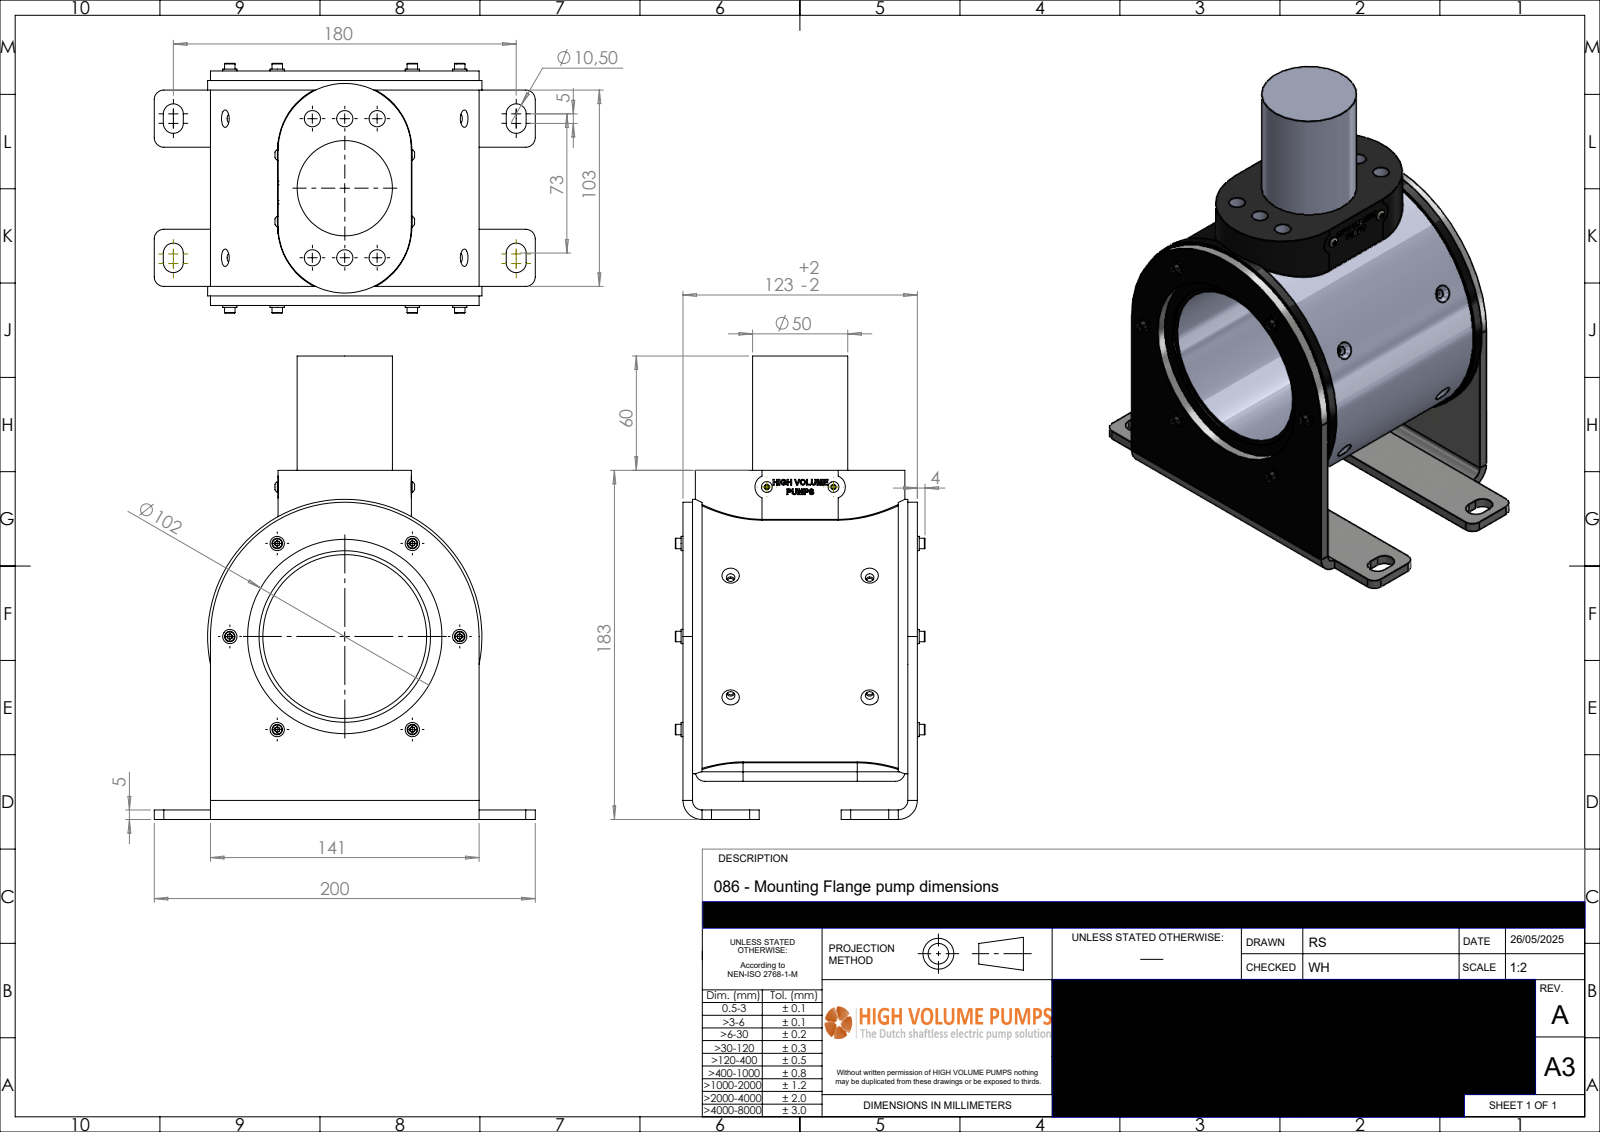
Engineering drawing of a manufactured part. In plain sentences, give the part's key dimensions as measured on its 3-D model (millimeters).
The part is named "P-086-030-rev-A-MF". Its 3-D file was written by "SolidWorks 2024 (AUTOMOTIVE_DESIGN)". It is 1 solid with 867 faces: 569 planar, 106 cylindrical and 192 other. Overall it measures 243.22 by 200 by 131.06 millimeters. Its volume is 1 580 000 cubic millimeters and its surface area 181 146 square millimeters. Round holes: 6 of diameter 8.5, 4 of diameter 3.3, 4 of diameter 4.5, 1 of diameter 86, 1 of diameter 90, 1 of diameter 102. Round bosses or shafts: 6 of diameter 7.5, 6 of diameter 5.5, 2 of diameter 7.64, 2 of diameter 5.7, 1 of diameter 144, 1 of diameter 141, 1 of diameter 50. Partial cylindrical surfaces (rounded edges, fillets, slot ends): 12 of radius 5, 8 of radius 5.25, 4 of radius 0.5, 2 of radius 2, 2 of radius 6.25, 2 of radius 10, 2 of radius 25, 2 of radius 35. The main face-to-face distances are 5, 118.06, 123.06, 113.06, 183.22, 178.22, 20, 15, 163.22, 60. The hole center spacings are 73, 17, 74.95, 34, 80.53.
